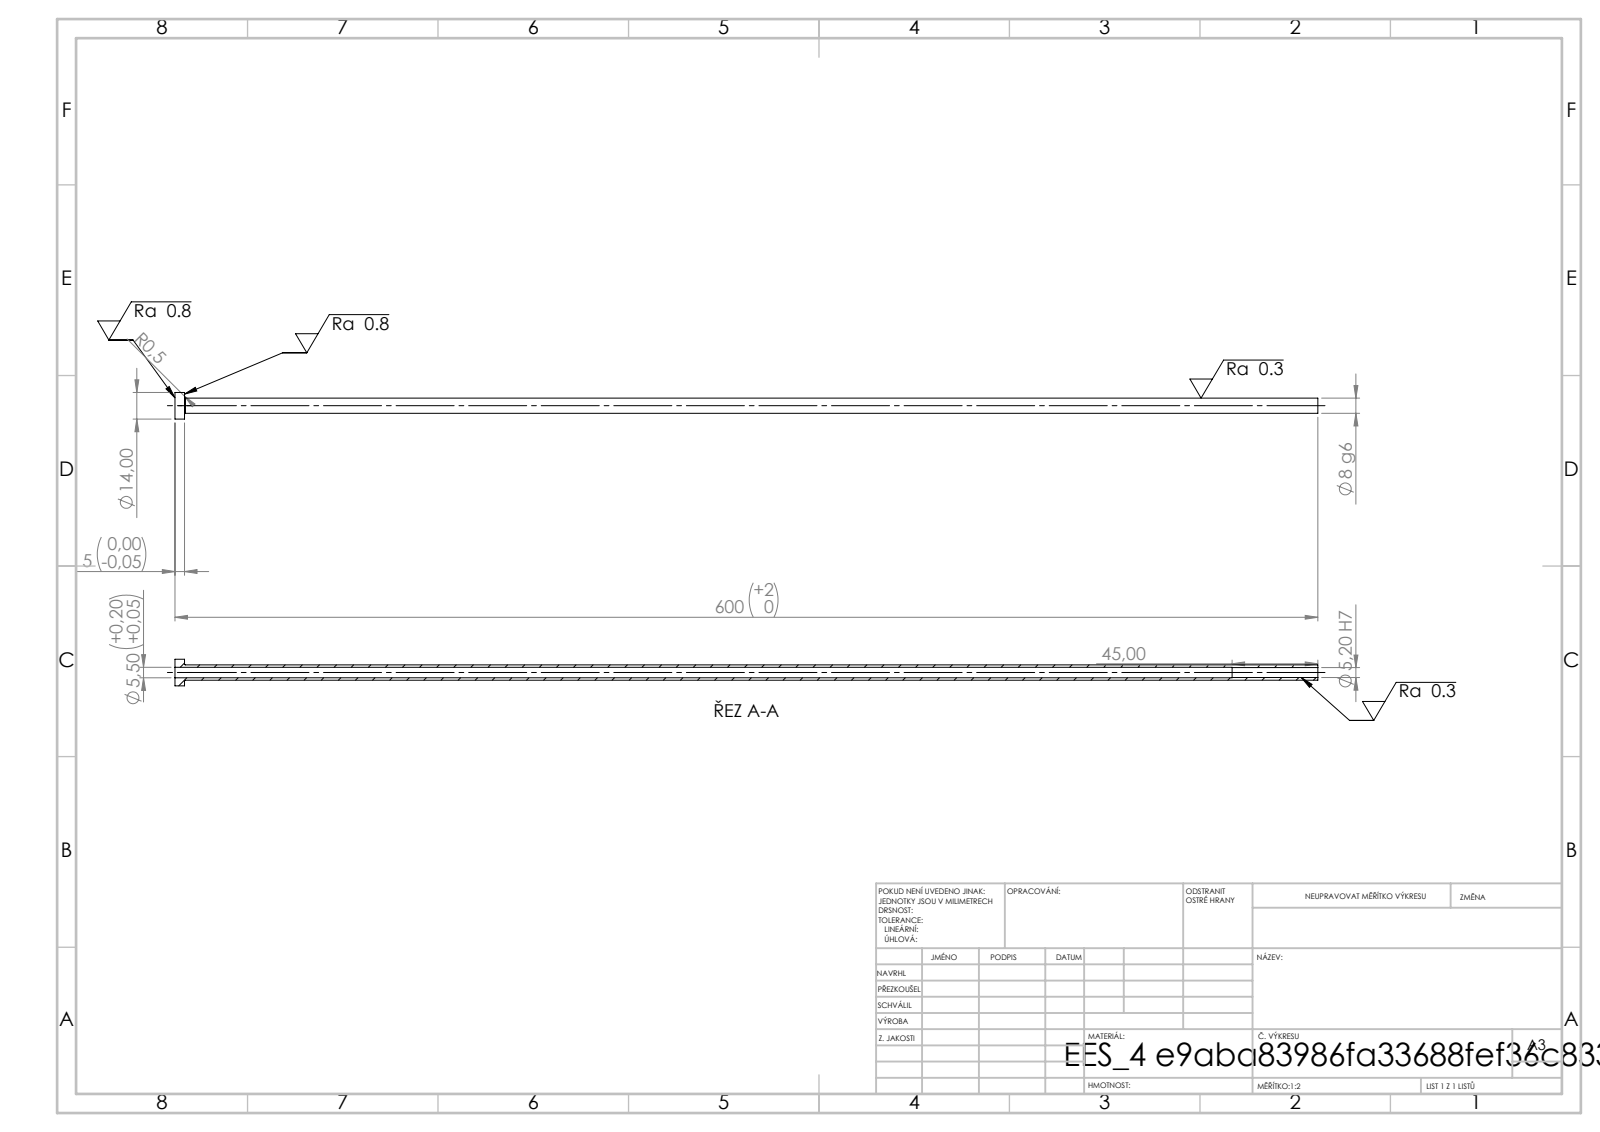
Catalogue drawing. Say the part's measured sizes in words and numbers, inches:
Its 3-D file was written by "SolidWorks 2019 (CONFIG_CONTROL_DESIGN)". It is 1 solid with 14 faces: 4 planar, 8 cylindrical and 2 other. Overall it measures 23.622 by 0.551 by 0.551 inches. Its volume is 1.009 cubic inches and its surface area 39.93 square inches. Round holes: 1 of diameter 0.205, 1 of diameter 0.217. Round bosses or shafts: 1 of diameter 0.551, 1 of diameter 0.315. The main face-to-face distances are 0.197, 23.622, 23.425, 21.85, 21.654, 1.772.
